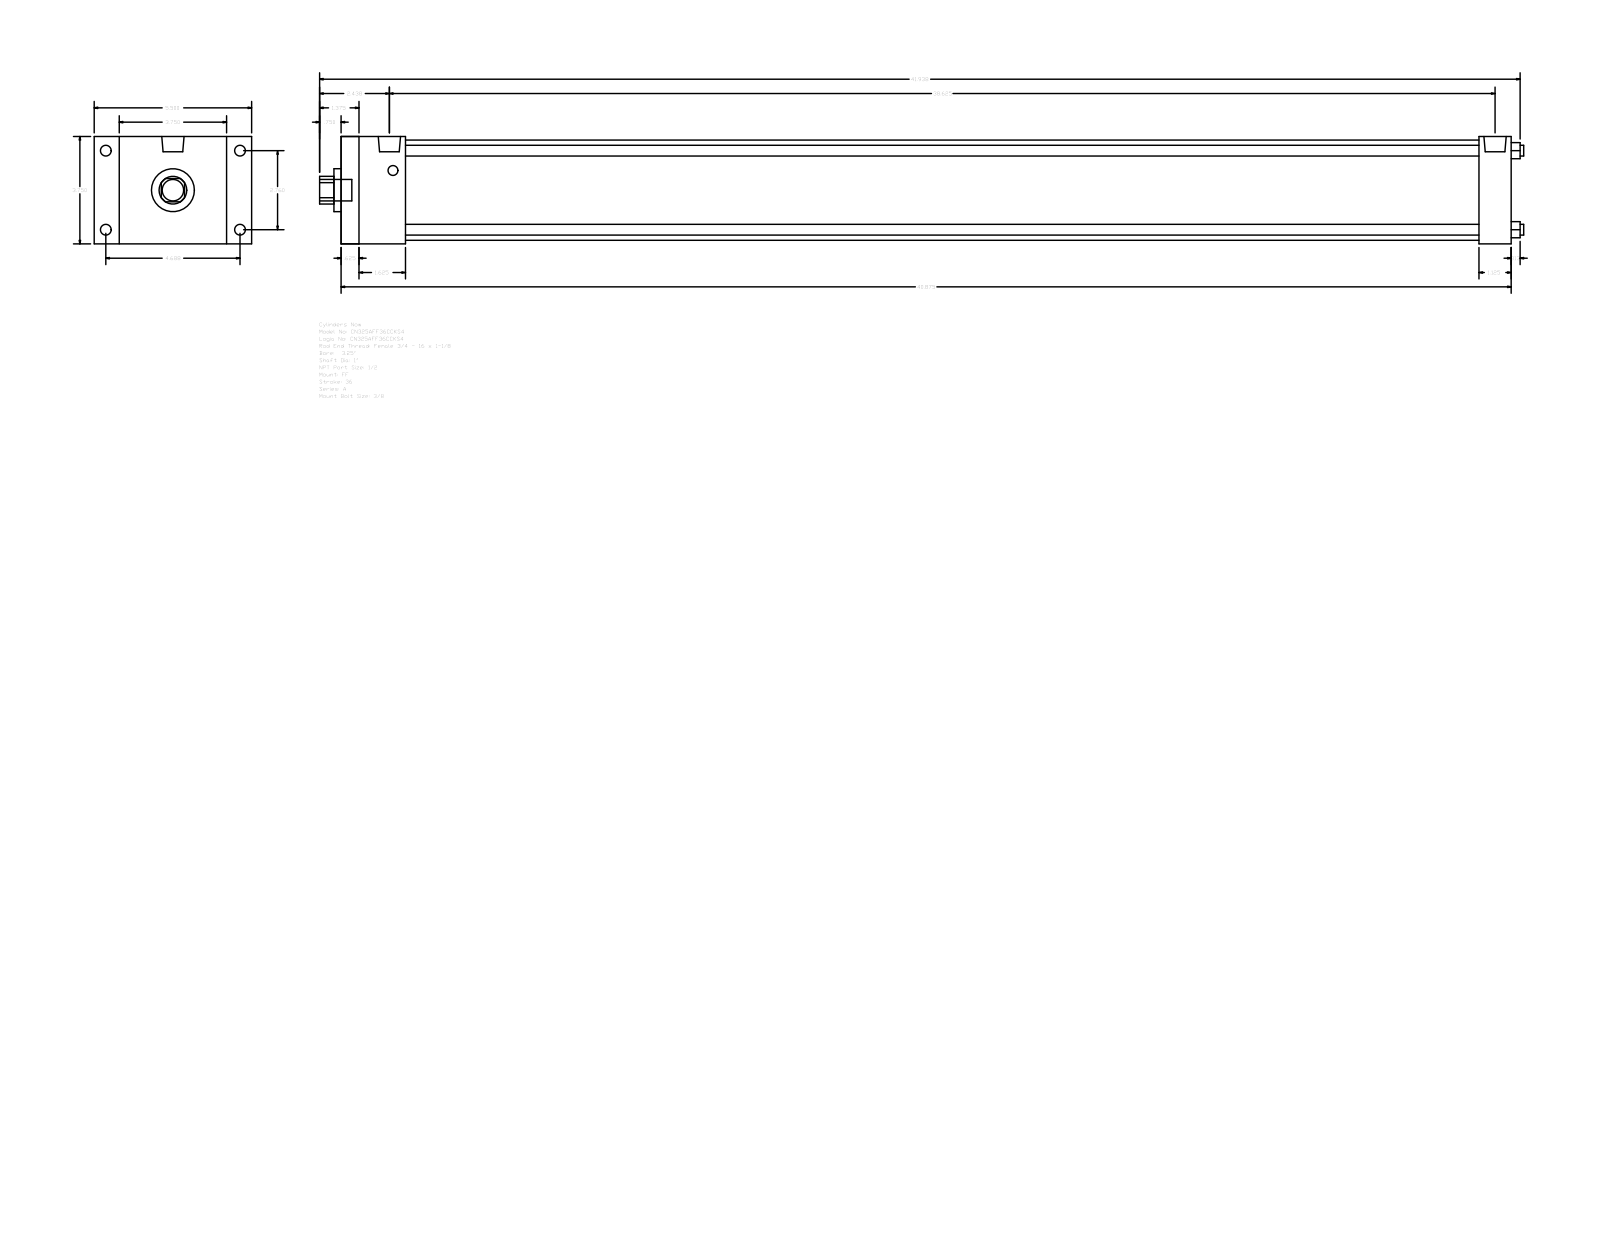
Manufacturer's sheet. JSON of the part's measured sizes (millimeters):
{"part_name": "A_FF__0325_1", "step_written_by": "GSSL Pune (CONFIG_CONTROL_DESIGN)", "units": "millimeters", "bodies": {"solids": 0, "faces": 92, "planar": 64, "cylindrical": 28, "other": 0}, "overall_size": [1068.39, 139.7, 95.25], "round_holes": [[9.53, 4], [25.4, 1], [38.1, 1], [88.9, 1]], "round_bosses_or_shafts": [[9.53, 4], [8.73, 4], [19.77, 2], [19.05, 1]], "partial_cylinders_radius": [[12.29, 1]], "face_to_face_distances": [95.24, 1038.23, 15.87, 1022.36, 22.23, 117.47, 57.15, 1009.65, 41.28, 993.78], "hole_center_spacings": [49.57, 70.1, 99.14]}
